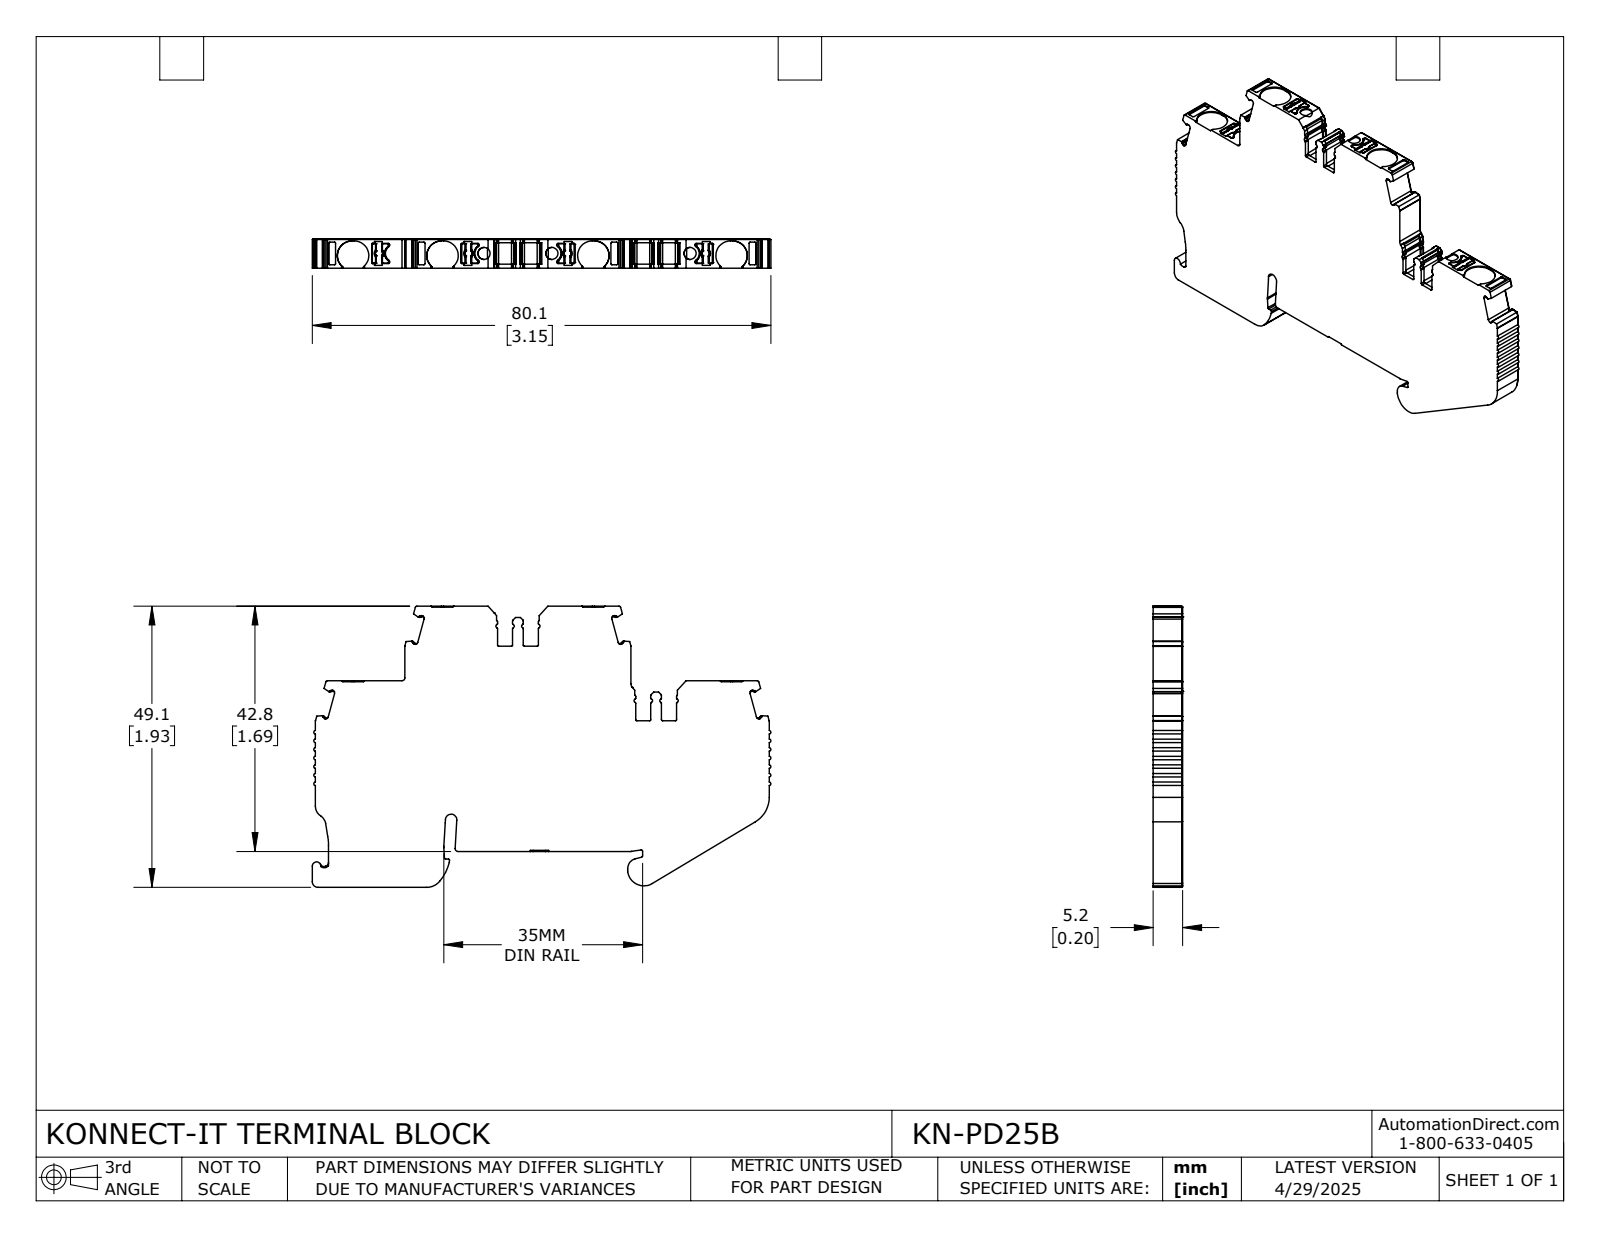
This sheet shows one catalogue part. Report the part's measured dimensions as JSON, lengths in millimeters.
{"part_name": "KN-PD25B", "step_written_by": "SolidWorks 2024 (CONFIG_CONTROL_DESIGN)", "units": "millimeters", "bodies": {"solids": 1, "faces": 977, "planar": 472, "cylindrical": 438, "other": 67}, "overall_size": [80.09, 49.09, 5.15], "volume_mm3": 14572, "surface_area_mm2": 7506, "round_holes": [[2.1, 3]], "partial_cylinders_radius": [[0.2, 100], [0.3, 57], [0.1, 41], [0.5, 21], [0.4, 17], [0.15, 16], [0.6, 9], [0.16, 8]], "face_to_face_distances": [5.15, 13.01, 6.26, 42.62, 29.61, 48.88, 2, 35.87, 12.81, 24.14], "hole_center_spacings": [11.84, 24.14, 35.98]}
